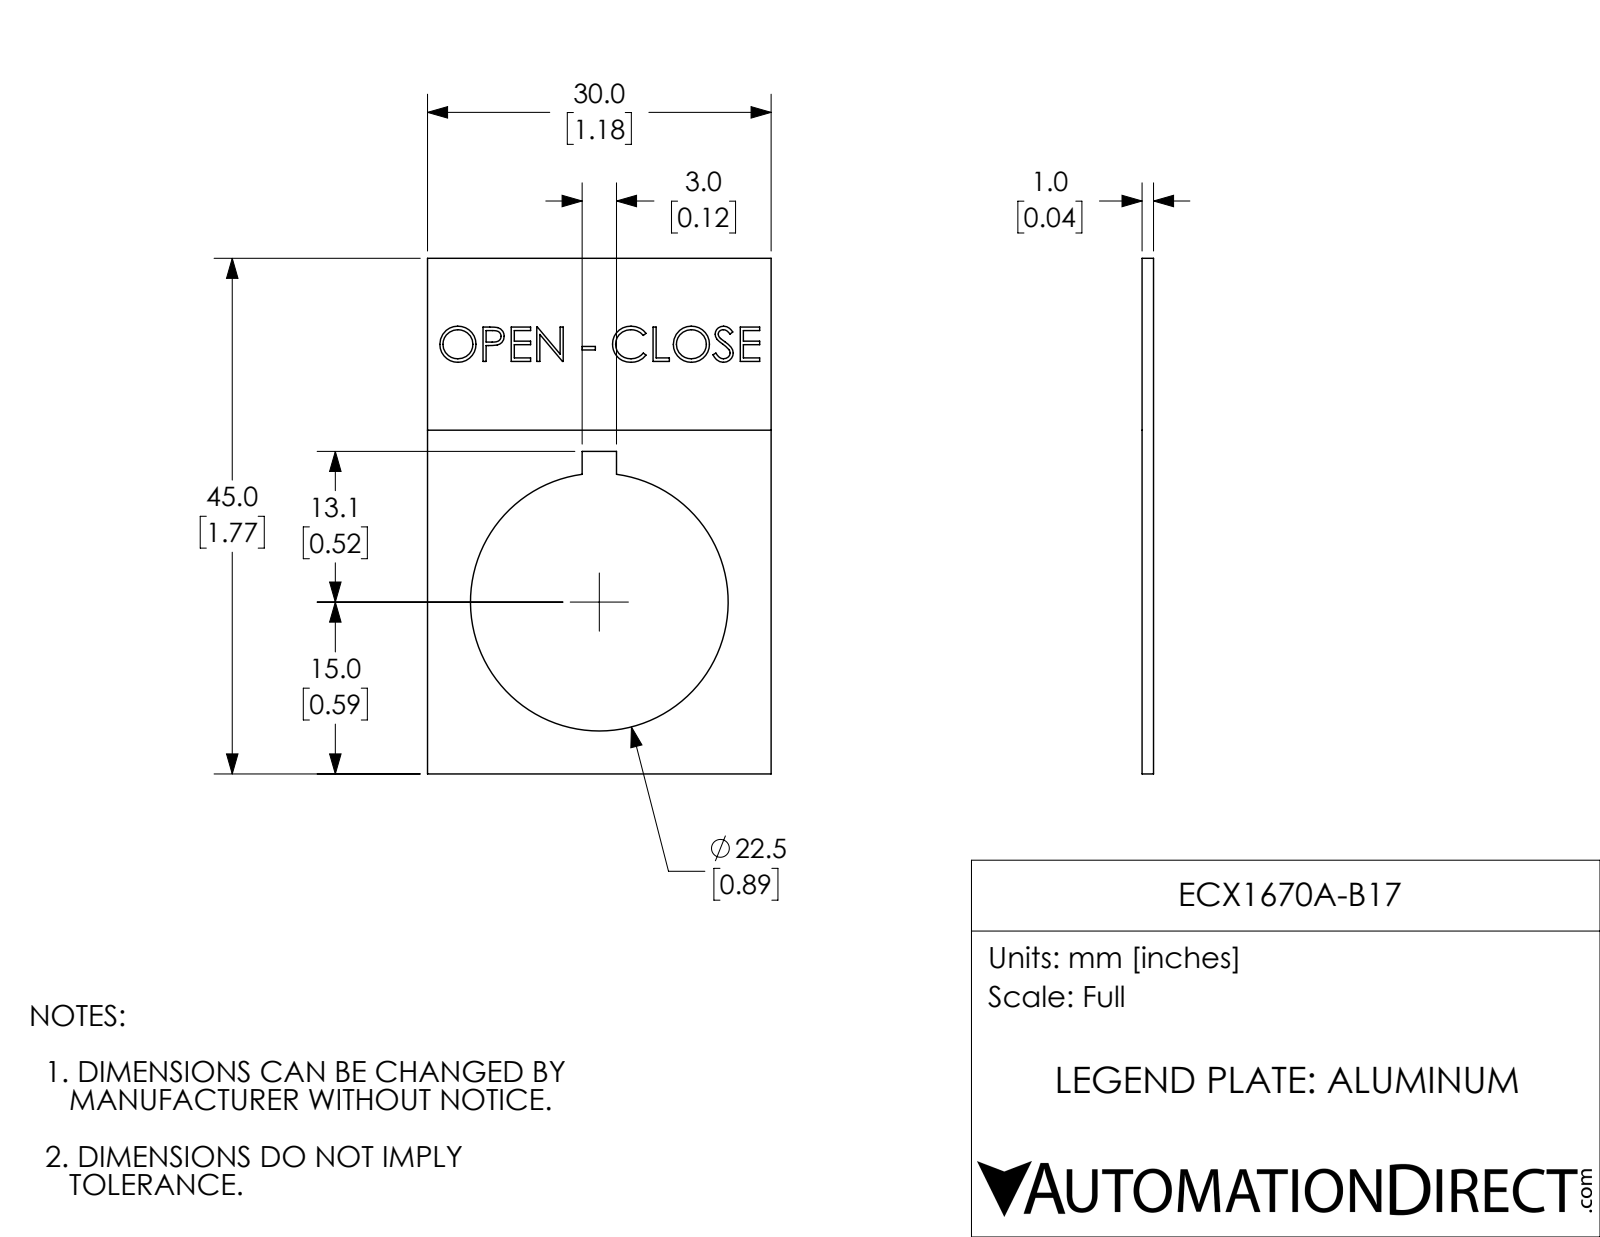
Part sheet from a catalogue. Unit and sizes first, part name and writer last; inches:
Units: inches
Overall size (bounding box): 1.772 × 1.181 × 0.039
Round holes (diameter × count): ⌀0.886 ×1
Main face-to-face distances: 0.039, 1.181, 1.772, 0.038, 0.531, 0.65, 1.108, 0.663, 0.118, 0.012
Volume: 0.058 in³ · Surface area: 3.288 in²
Bodies: 1 solid, 128 faces (79 planar, 3 cylindrical, 46 other)
Part name (STEP PRODUCT): ECX1670A-B17
STEP written by: SolidWorks 2017 (AUTOMOTIVE_DESIGN)
